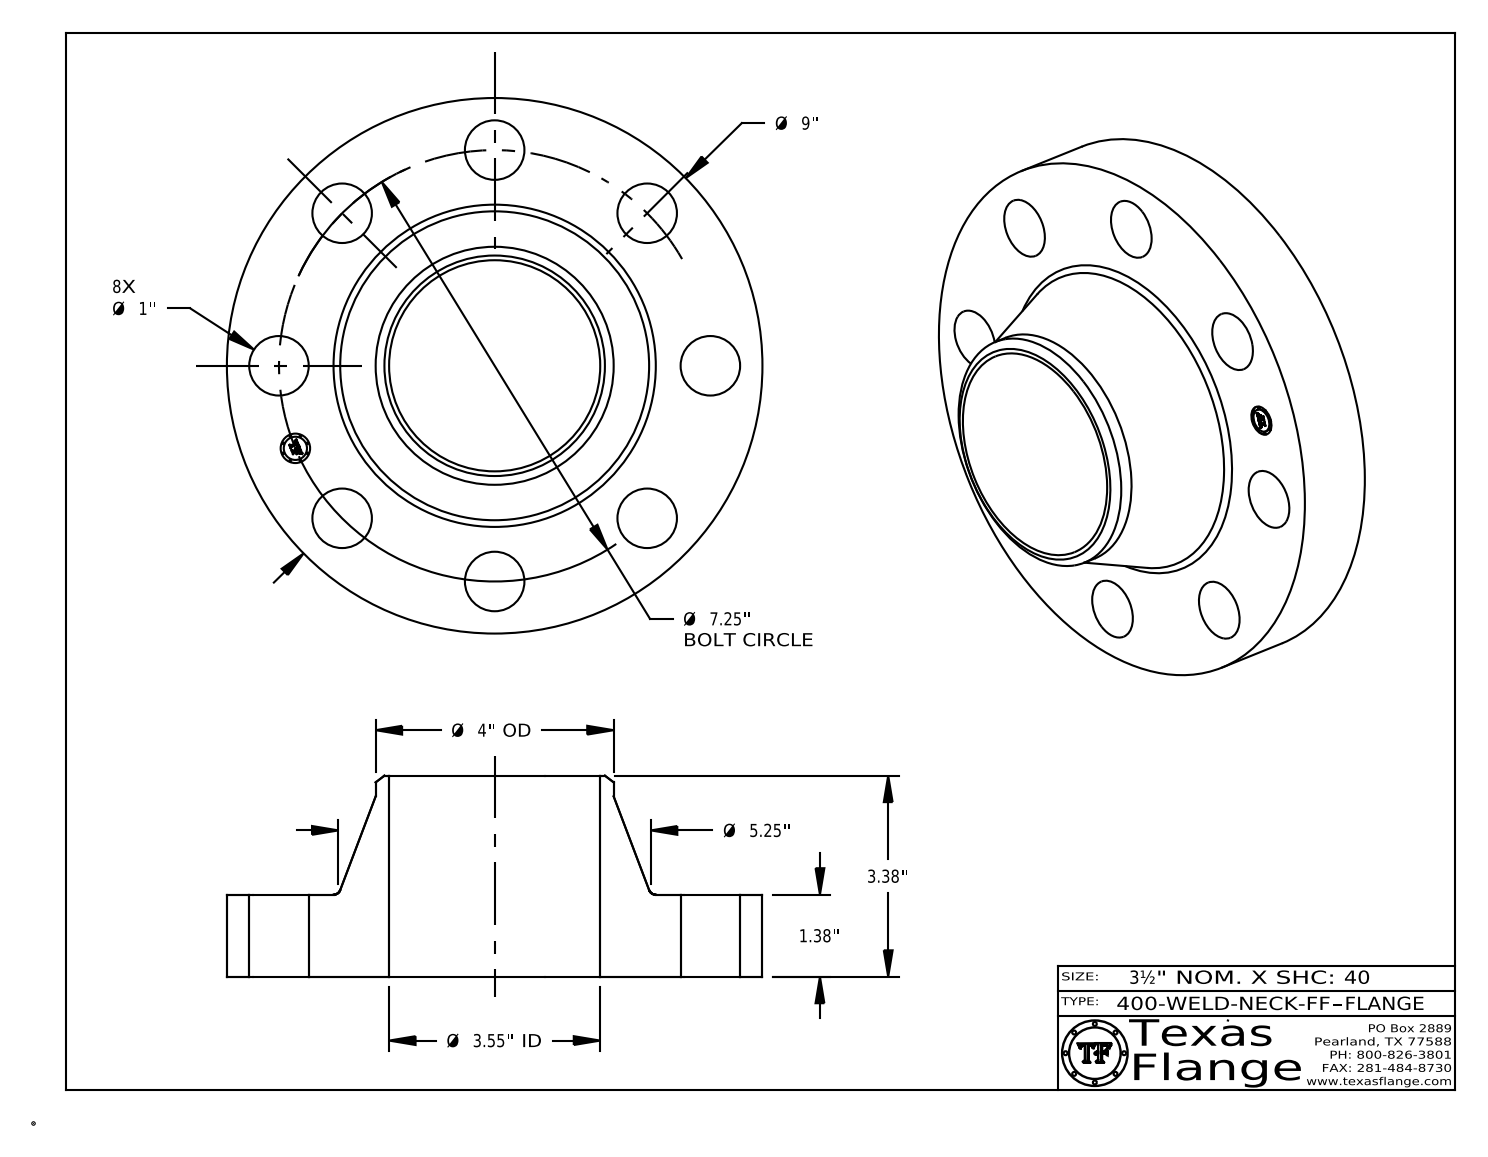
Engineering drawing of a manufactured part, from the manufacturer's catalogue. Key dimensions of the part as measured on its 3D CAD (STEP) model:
Part name (STEP PRODUCT): 400-WELD-NECK-FF
STEP written by: CATIA V5 STEP AP214 (AUTOMOTIVE_DESIGN)
Units: inches
Bodies: 1 solid, 416 faces (368 planar, 42 cylindrical, 6 other)
Overall size (bounding box): 9 × 9 × 3.38
Volume: 77.91 in³ · Surface area: 226 in²
Round holes (diameter × count): ⌀1 ×8, ⌀0.495 ×1, ⌀3.548 ×1
Round bosses / shafts (diameter × count): ⌀0.03 ×8, ⌀9 ×1, ⌀4 ×1, ⌀0.39 ×1
Main face-to-face distances: 1.38, 3.38, 2, 1.365, 0.015, 2.015, 0.148, 0.144, 0.027, 0.096
Hole centre spacings: 3.625, 2.774, 5.127, 6.698, 7.25, 1.415, 7.111, 4.028
